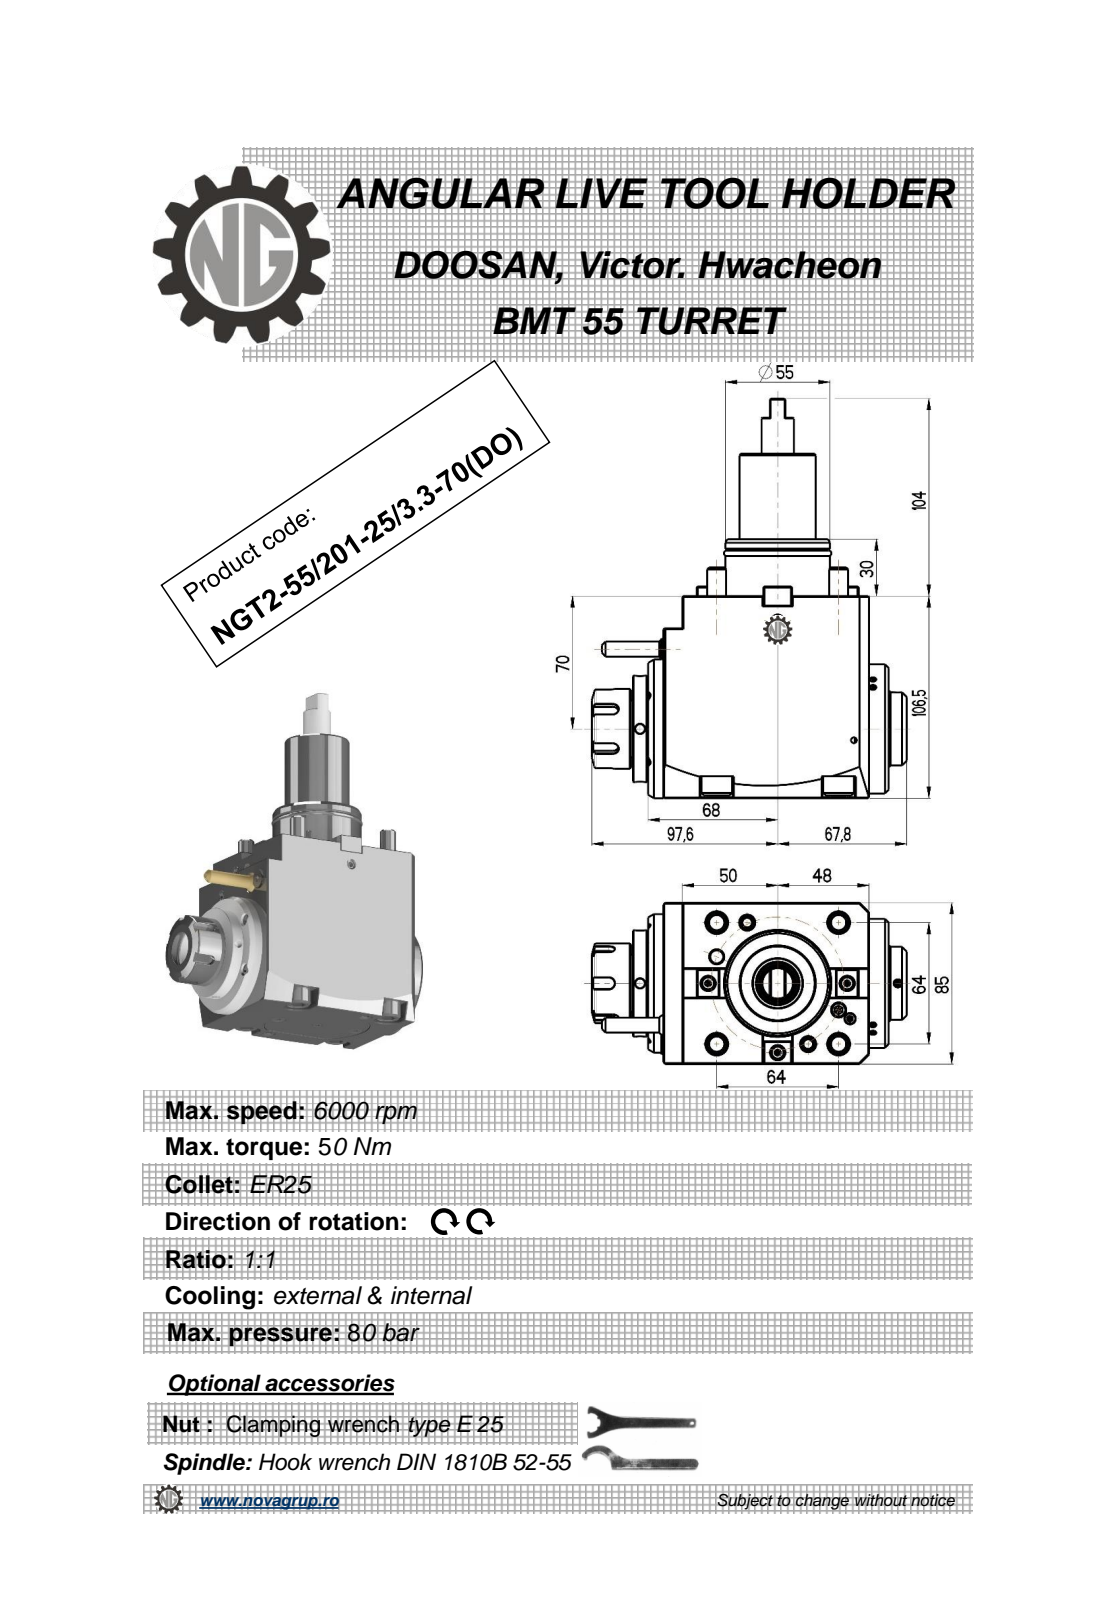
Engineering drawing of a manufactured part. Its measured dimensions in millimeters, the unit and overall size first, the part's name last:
Units: millimetres
Overall size (bounding box): 210.5 × 165.4 × 85
Round holes (diameter × count): ⌀5 ×3, ⌀6.8 ×2, ⌀3 ×1, ⌀12 ×1
Round bosses / shafts (diameter × count): ⌀16 ×4, ⌀10 ×4, ⌀73 ×1, ⌀68 ×1, ⌀56 ×1, ⌀55 ×1, ⌀50 ×1, ⌀43.4 ×1
Partial cylindrical surfaces — rounded edges, fillets, slot ends (radius × count): R0.32 ×20, R0.22 ×6, R3 ×5, R8.5 ×4, R0.8 ×2, R480 ×2
Main face-to-face distances: 85, 106.5, 8, 108, 116, 16, 10, 126.3, 118.3, 10.3
Hole centre spacings: 42.62, 69.86, 105.19
Volume: 1 205 000 mm³ · Surface area: 106 702 mm²
Bodies: 2 solids, 489 faces (229 planar, 111 cylindrical, 149 other)
Part name (STEP PRODUCT): NGT2_55_201_25_3_3_70_DO
STEP written by: PRO/ENGINEER BY PARAMETRIC TECHNOLOGY CORPORATION, 2010280 (CONFIG_CONTROL_DESIGN)
